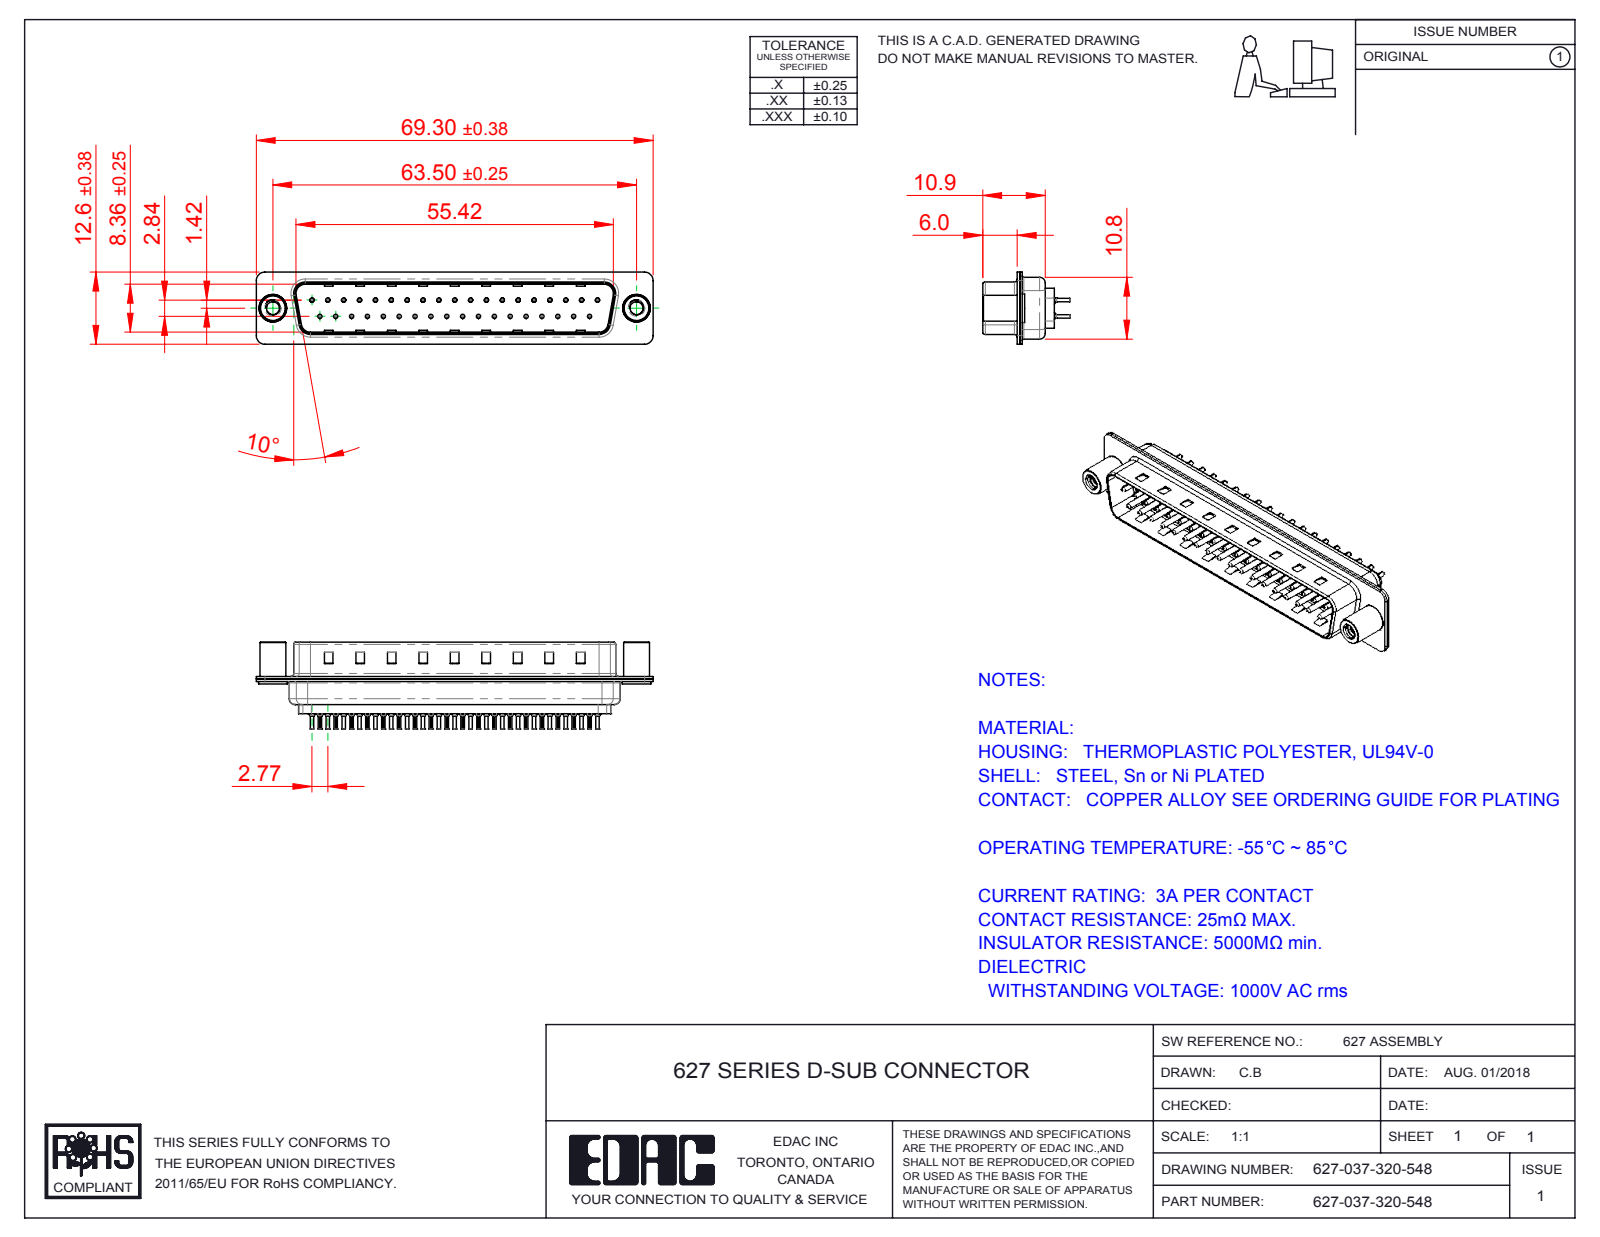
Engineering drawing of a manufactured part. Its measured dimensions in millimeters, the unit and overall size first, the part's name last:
Units: millimetres
Overall size (bounding box): 69.3 × 15.2 × 12.6
Round holes (diameter × count): ⌀0.2 ×37, ⌀0.35 ×37, ⌀1.1 ×37, ⌀1.6 ×37, ⌀2.26 ×2, ⌀4 ×2, ⌀4.8 ×2
Round bosses / shafts (diameter × count): ⌀2 ×37, ⌀1.5 ×37, ⌀0.75 ×37, ⌀0.6 ×37, ⌀5 ×2, ⌀4.9 ×2, ⌀4.5 ×2
Partial cylindrical surfaces — rounded edges, fillets, slot ends (radius × count): R0.1 ×74, R1.5 ×16, R2 ×12, R0.5 ×8, R1.6 ×8, R0.25 ×4, R0.6 ×4, R0.65 ×4
Main face-to-face distances: 0.4, 0.82, 9.58, 0.45, 8.76, 1.5, 0.9, 1.4, 6.05, 0.42
Hole centre spacings: 3.16, 2.77, 5.54, 8.31, 5.04, 10.1, 11.08, 12.78
Volume: 3 746 mm³ · Surface area: 10 657 mm²
Bodies: 42 solids, 4072 faces (1093 planar, 1538 cylindrical, 1441 other)
Part name (STEP PRODUCT): 627 Shell Front_37 Contacts; 627 Housing_37 LP; 627 4-40 Threaded Standoff; 627 Shell Rear_37 Contacts (+3 more)
STEP written by: SolidWorks 2016 (CONFIG_CONTROL_DESIGN)
